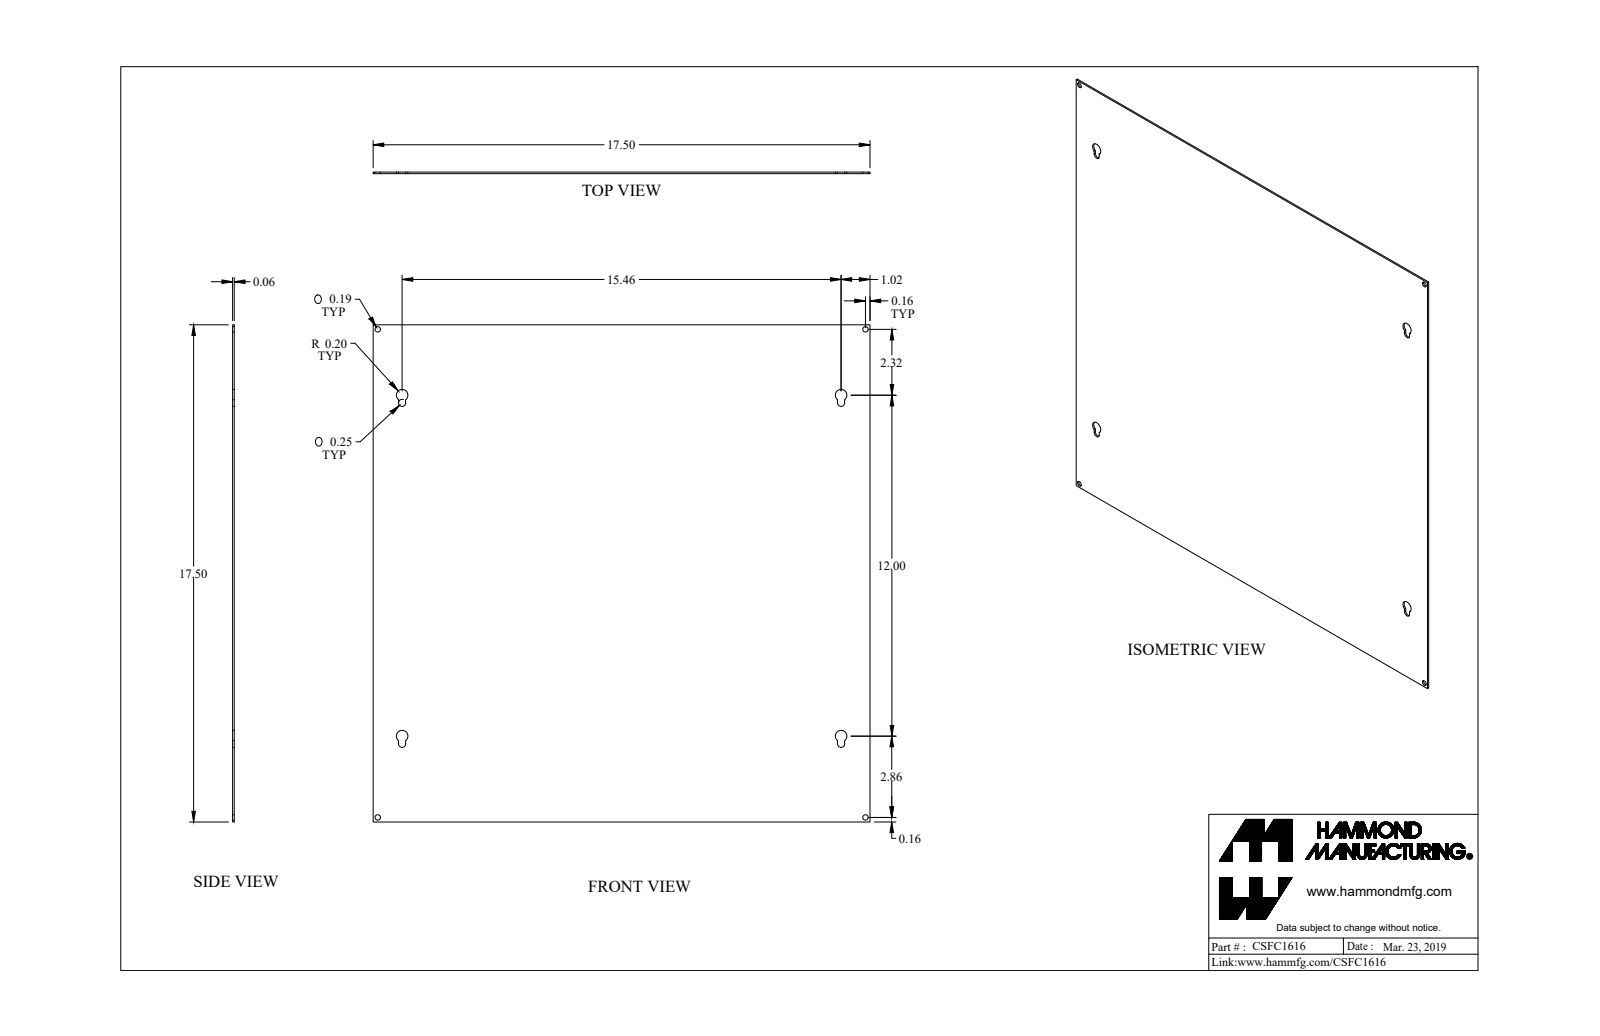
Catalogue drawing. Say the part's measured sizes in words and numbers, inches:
The part is named "CSFC1616_Default". Its 3-D file was written by "SolidWorks 2019 (CONFIG_CONTROL_DESIGN)". It is 1 solid with 38 faces: 14 planar, 24 cylindrical and 0 other. Overall it measures 17.5 by 17.5 by 0.057 inches. Its volume is 17.41 cubic inches and its surface area 615.4 square inches. Round holes: 4 of diameter 0.188. Partial cylindrical surfaces (rounded edges, fillets, slot ends): 4 of radius 0.125, 4 of radius 0.203. The main face-to-face distances are 0.057, 17.5, 0.895, 1.145, 16.355, 16.605, 15.46, 0.25, 15.71, 15.21. The hole center spacings are 17.18, 24.296.
